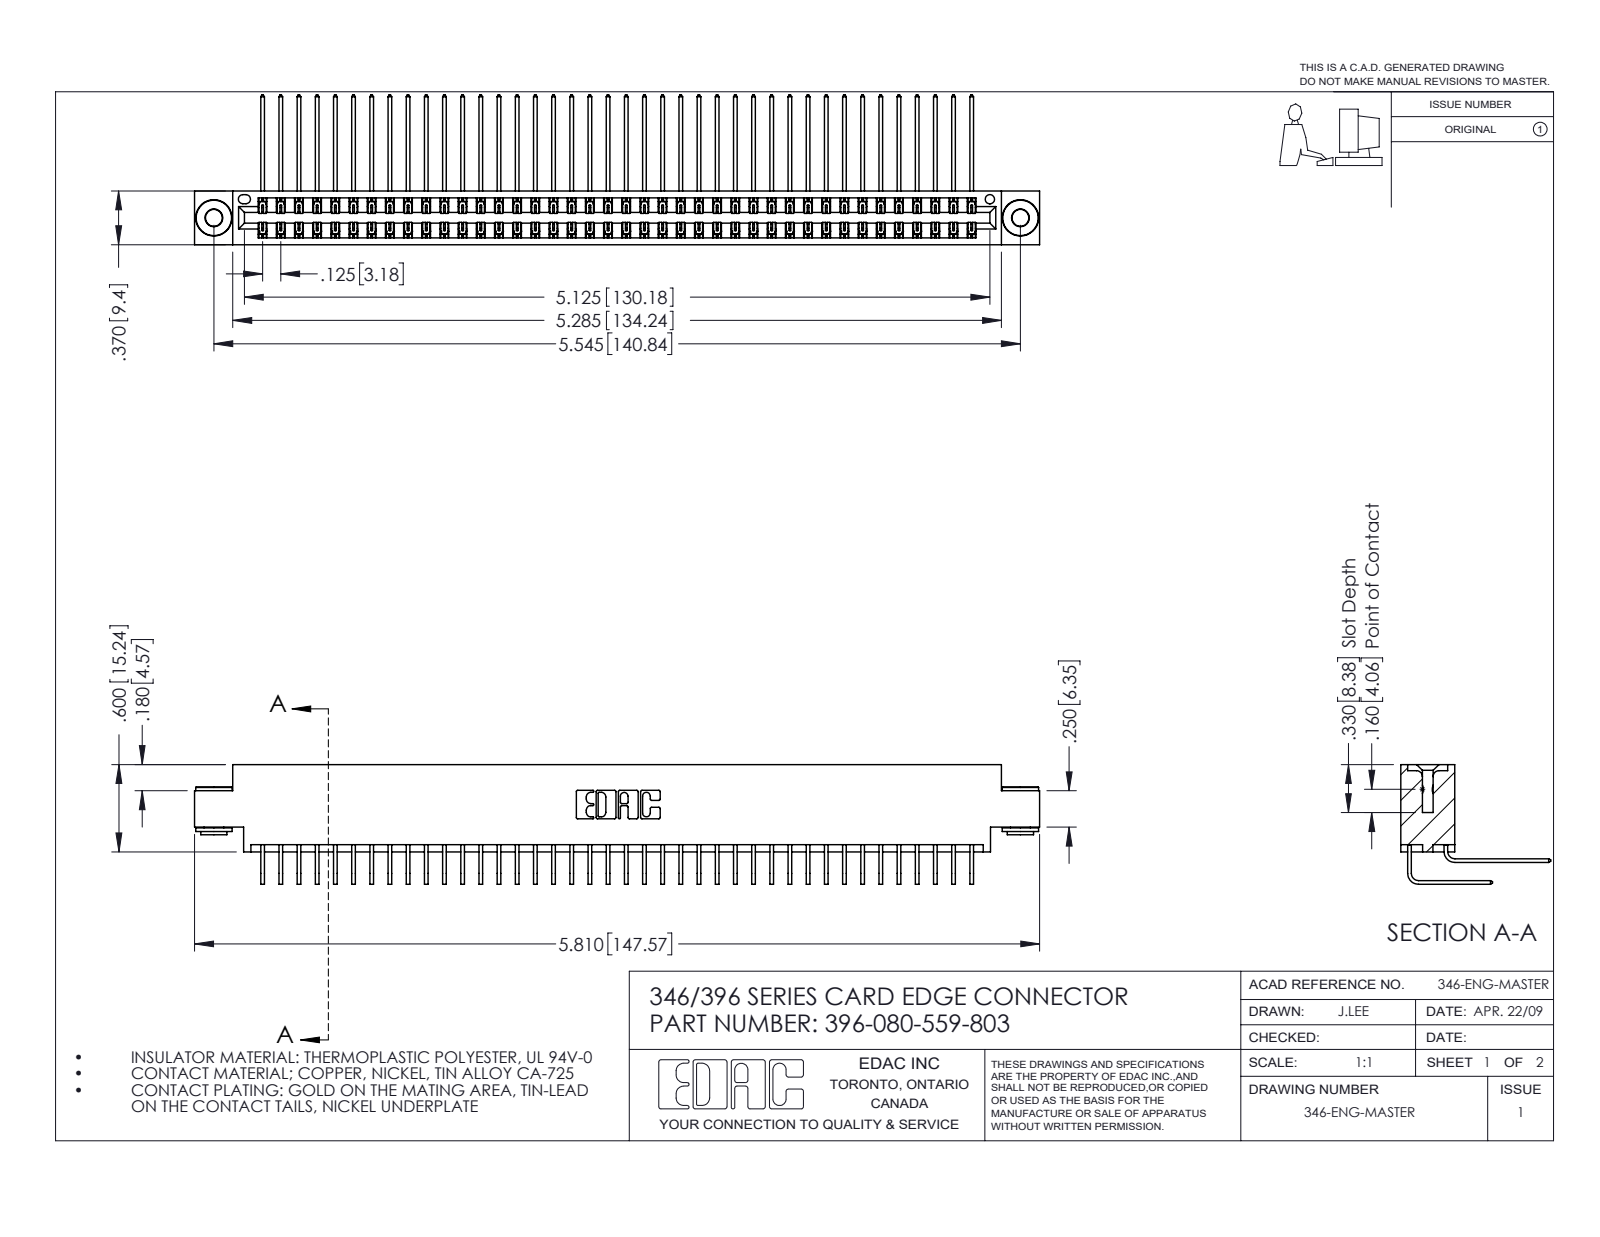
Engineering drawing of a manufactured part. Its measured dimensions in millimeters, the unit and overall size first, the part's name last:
Units: millimetres
Overall size (bounding box): 147.6 × 26.2 × 20.9
Round holes (diameter × count): ⌀2.9 ×2, ⌀4 ×2, ⌀1.6 ×1
Round bosses / shafts (diameter × count): ⌀6.4 ×2, ⌀4.6 ×2, ⌀3.5 ×2
Partial cylindrical surfaces — rounded edges, fillets, slot ends (radius × count): R0.2 ×120, R0.3 ×22, R0.2 ×6, R0.8 ×6, R0.7 ×3, R0.4 ×2, R0.6 ×2, R0.6 ×2
Main face-to-face distances: 1.2, 8.2, 0.6, 9.4, 6.4, 1.8, 7.6, 7, 3.8, 5.6
Hole centre spacings: 6.2, 135.5, 140.8
Volume: 14 700 mm³ · Surface area: 22 790 mm²
Bodies: 83 solids, 4484 faces (3050 planar, 1426 cylindrical, 8 other)
Part name (STEP PRODUCT): 345-292-001_558 559 Tail - 1; 345-250-002_345-250-002-102; 396-080-559-803; 345-292-001_559 Tail - 2 (+1 more)
STEP written by: SolidWorks 2016 (CONFIG_CONTROL_DESIGN)
